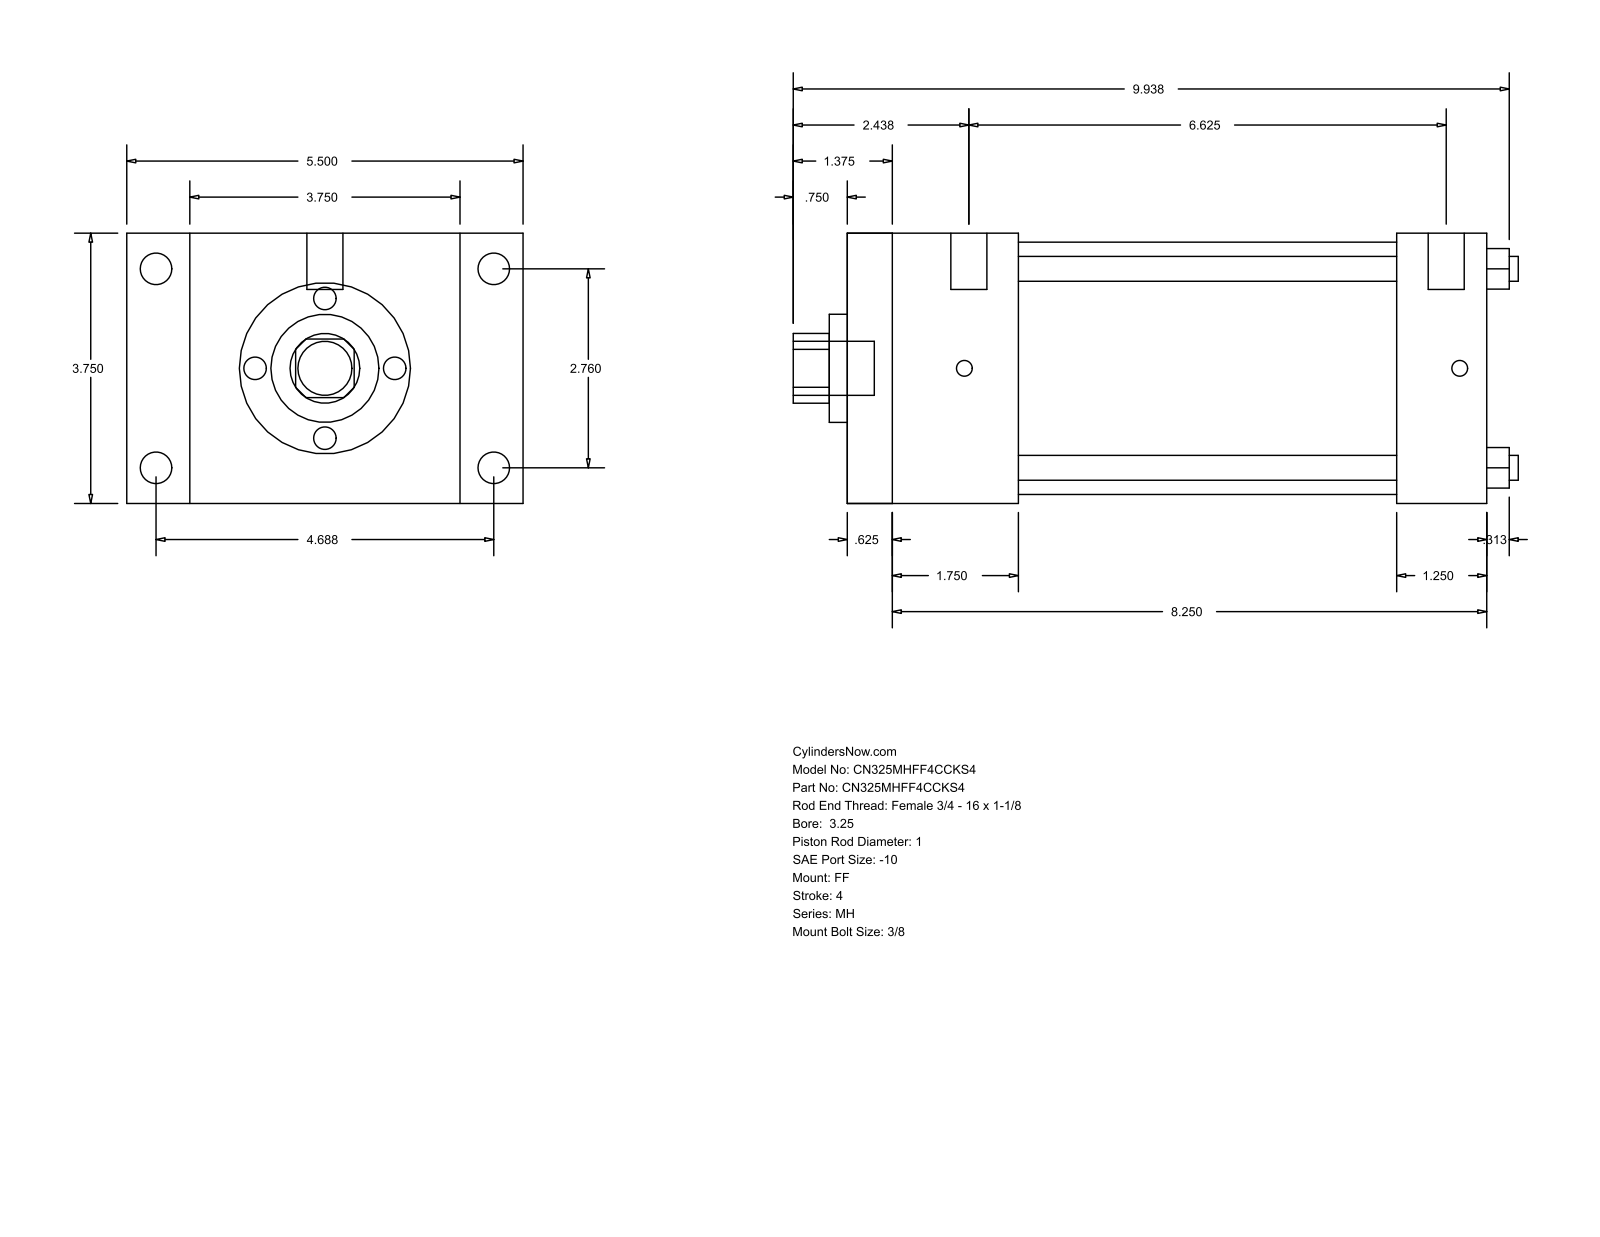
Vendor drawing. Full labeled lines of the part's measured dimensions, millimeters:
Part name (STEP PRODUCT): MH_FF__0325_1
STEP written by: GSSL Pune (CONFIG_CONTROL_DESIGN)
Units: millimetres
Bodies: 0 solids, 92 faces (64 planar, 28 cylindrical, 0 other)
Overall size (bounding box): 255.59 × 139.7 × 95.25
Round holes (diameter × count): ⌀8.76 ×4, ⌀25.4 ×1, ⌀38.1 ×1, ⌀88.9 ×1
Round bosses / shafts (diameter × count): ⌀11.13 ×4, ⌀5.56 ×4, ⌀12.7 ×2, ⌀19.05 ×1
Partial cylindrical surfaces — rounded edges, fillets, slot ends (radius × count): R12.29 ×1
Main face-to-face distances: 95.24, 225.42, 15.87, 209.55, 22.23, 117.47, 193.67, 177.8, 31.75, 60.33
Hole centre spacings: 49.57, 70.1, 99.14
